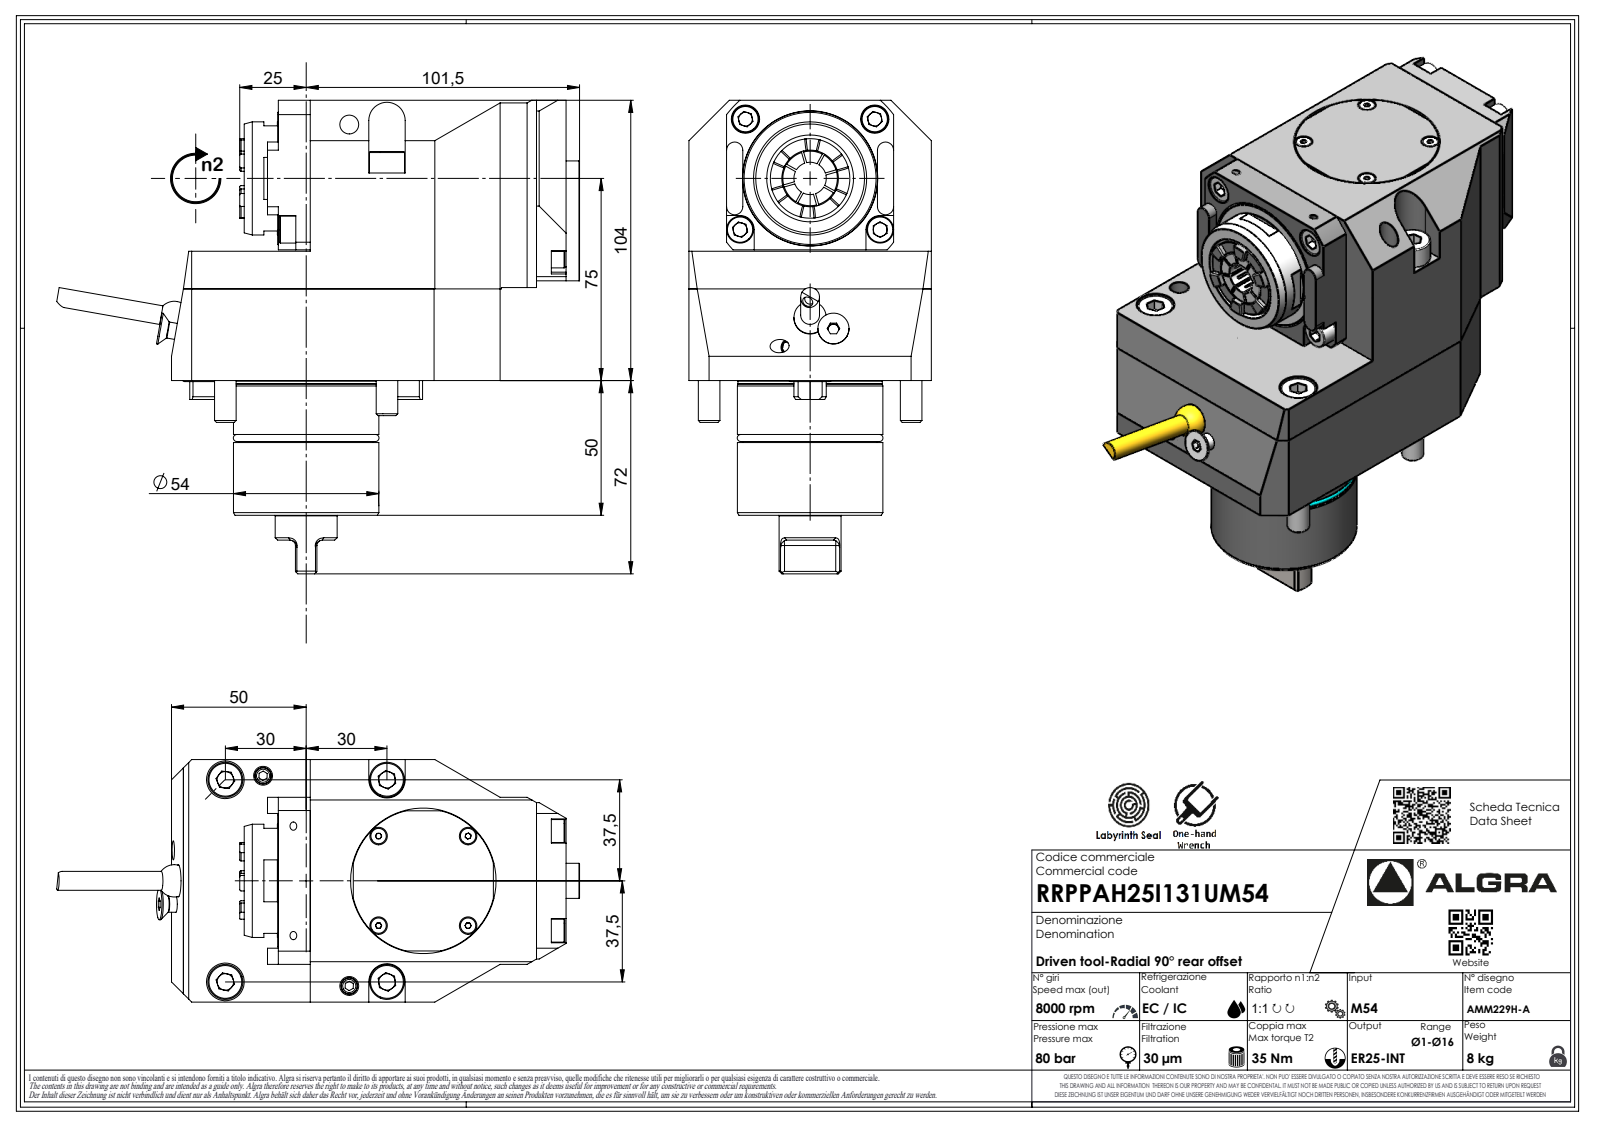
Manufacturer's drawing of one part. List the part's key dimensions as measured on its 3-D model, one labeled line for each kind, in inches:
Part name (STEP PRODUCT): RRPPAH25I131UM54
STEP written by: SolidWorks 2023 (AUTOMOTIVE_DESIGN)
Units: inches
Bodies: 1 solid, 511 faces (346 planar, 67 cylindrical, 98 other)
Overall size (bounding box): 7.643 × 6.917 × 3.543
Volume: 67 in³ · Surface area: 125.2 in²
Round holes (diameter × count): ⌀0.083 ×1, ⌀0.157 ×1
Round bosses / shafts (diameter × count): ⌀0.315 ×4, ⌀0.512 ×2, ⌀2.126 ×1, ⌀2.11 ×1, ⌀1.965 ×1, ⌀1.654 ×1, ⌀0.906 ×1, ⌀0.276 ×1
Partial cylindrical surfaces — rounded edges, fillets, slot ends (radius × count): R0.013 ×7, R0.02 ×7, R0.079 ×7, R0.146 ×7, R0.118 ×4, R0.236 ×2, R0.266 ×2, R0.008 ×1
Main face-to-face distances: 4.094, 3.543, 1.89, 2.205, 0.965, 0.551, 2.992, 3.74, 1.969, 3.858
